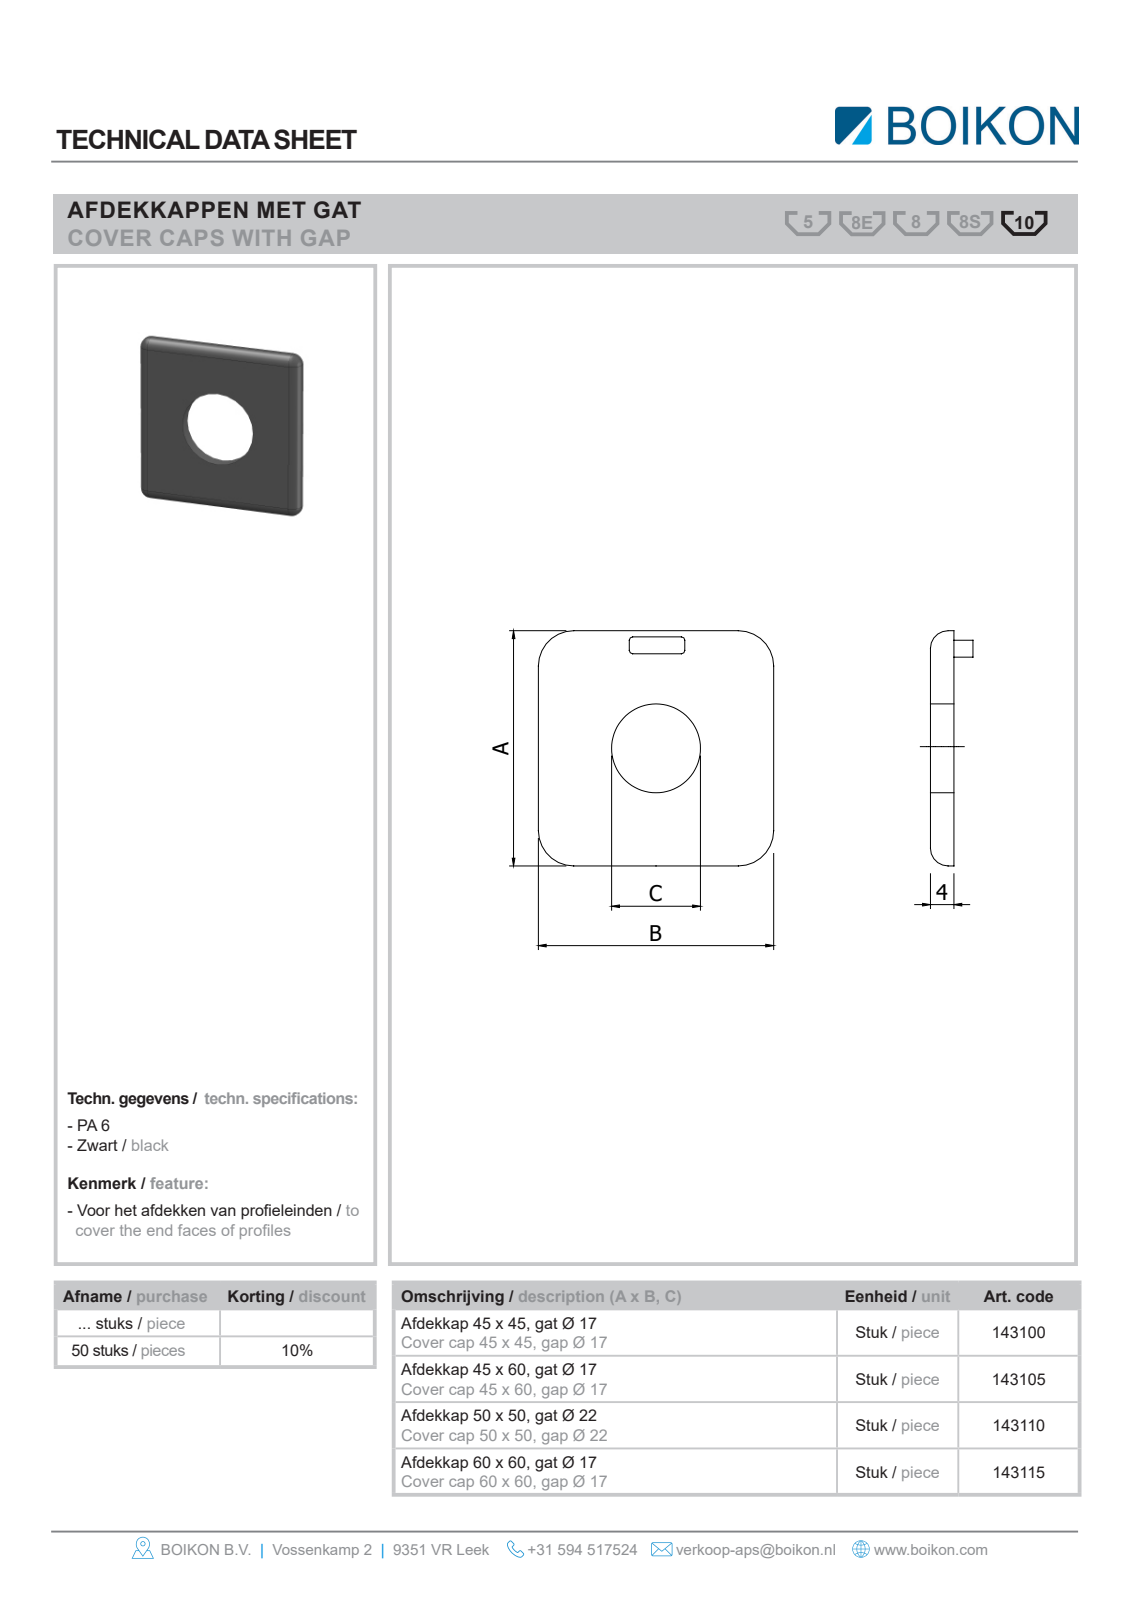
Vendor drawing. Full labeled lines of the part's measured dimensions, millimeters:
Part name (STEP PRODUCT): Root; 143100Afdekkap 45 x 45, gat rond 17BOIKON
STEP written by: HiCAD 2013 1802.4 Build 509 (AUTOMOTIVE_DESIGN)
Units: millimetres
Bodies: 1 solid, 19 faces (6 planar, 9 cylindrical, 4 other)
Overall size (bounding box): 45 × 45 × 4
Volume: 6 832 mm³ · Surface area: 4 264 mm²
Round holes (diameter × count): ⌀17 ×1
Partial cylindrical surfaces — rounded edges, fillets, slot ends (radius × count): R3 ×8
Main face-to-face distances: 4, 45
